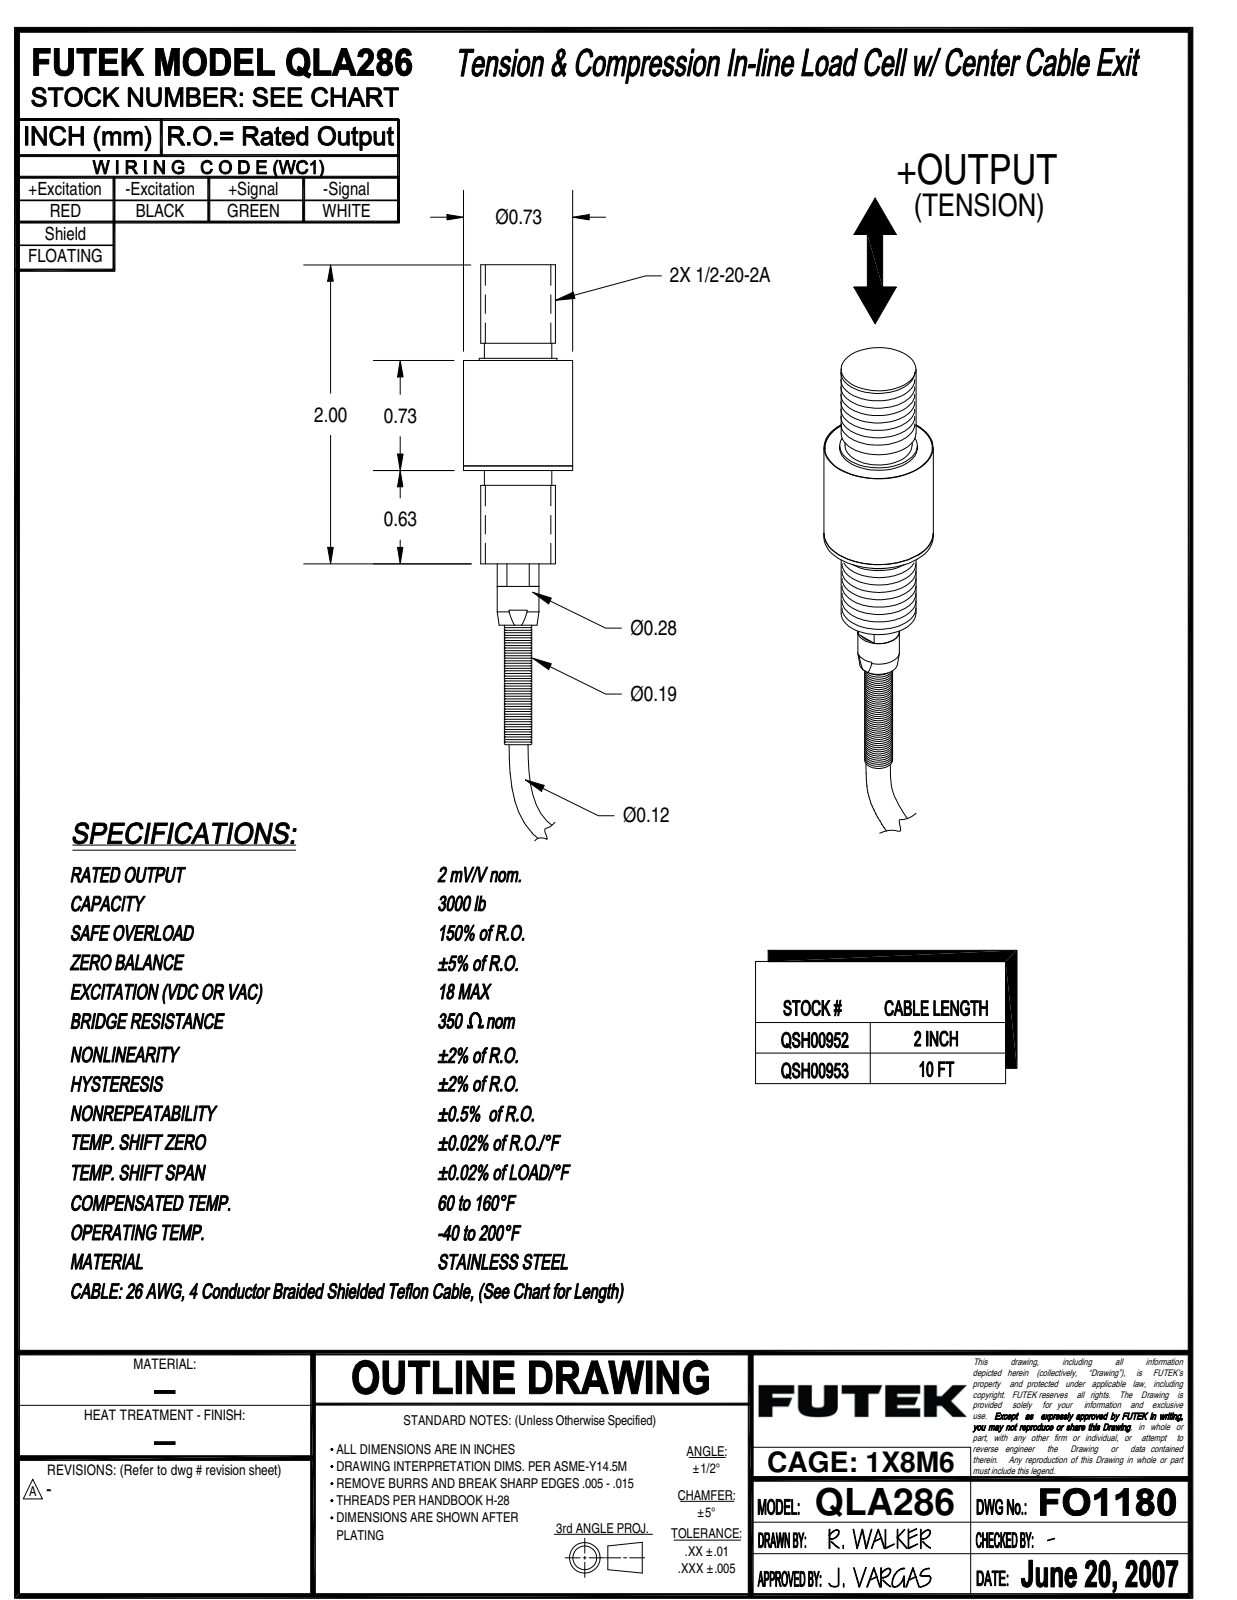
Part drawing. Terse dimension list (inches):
name: QLA286
written by: Autodesk Inventor 2020 (AUTOMOTIVE_DESIGN)
unit: in
bodies: 1 solid, 784 faces (302 planar, 142 cylindrical, 340 other)
size: 5.79 × 0.73 × 0.73
volume: 0.616 in³; area: 8.737 in²
holes: 1× ⌀0.521, 1× ⌀0.721
bosses: 1× ⌀0.73, 1× ⌀0.72, 1× ⌀0.519, 1× ⌀0.495, 1× ⌀0.441, 1× ⌀0.429, 1× ⌀0.278, 1× ⌀0.277
rounds: 1× R0.364
face distances: 0.73, 1.38, 0.65, 0.736, 0.644, 0.62, 1.35, 1.356, 2, 0.405
